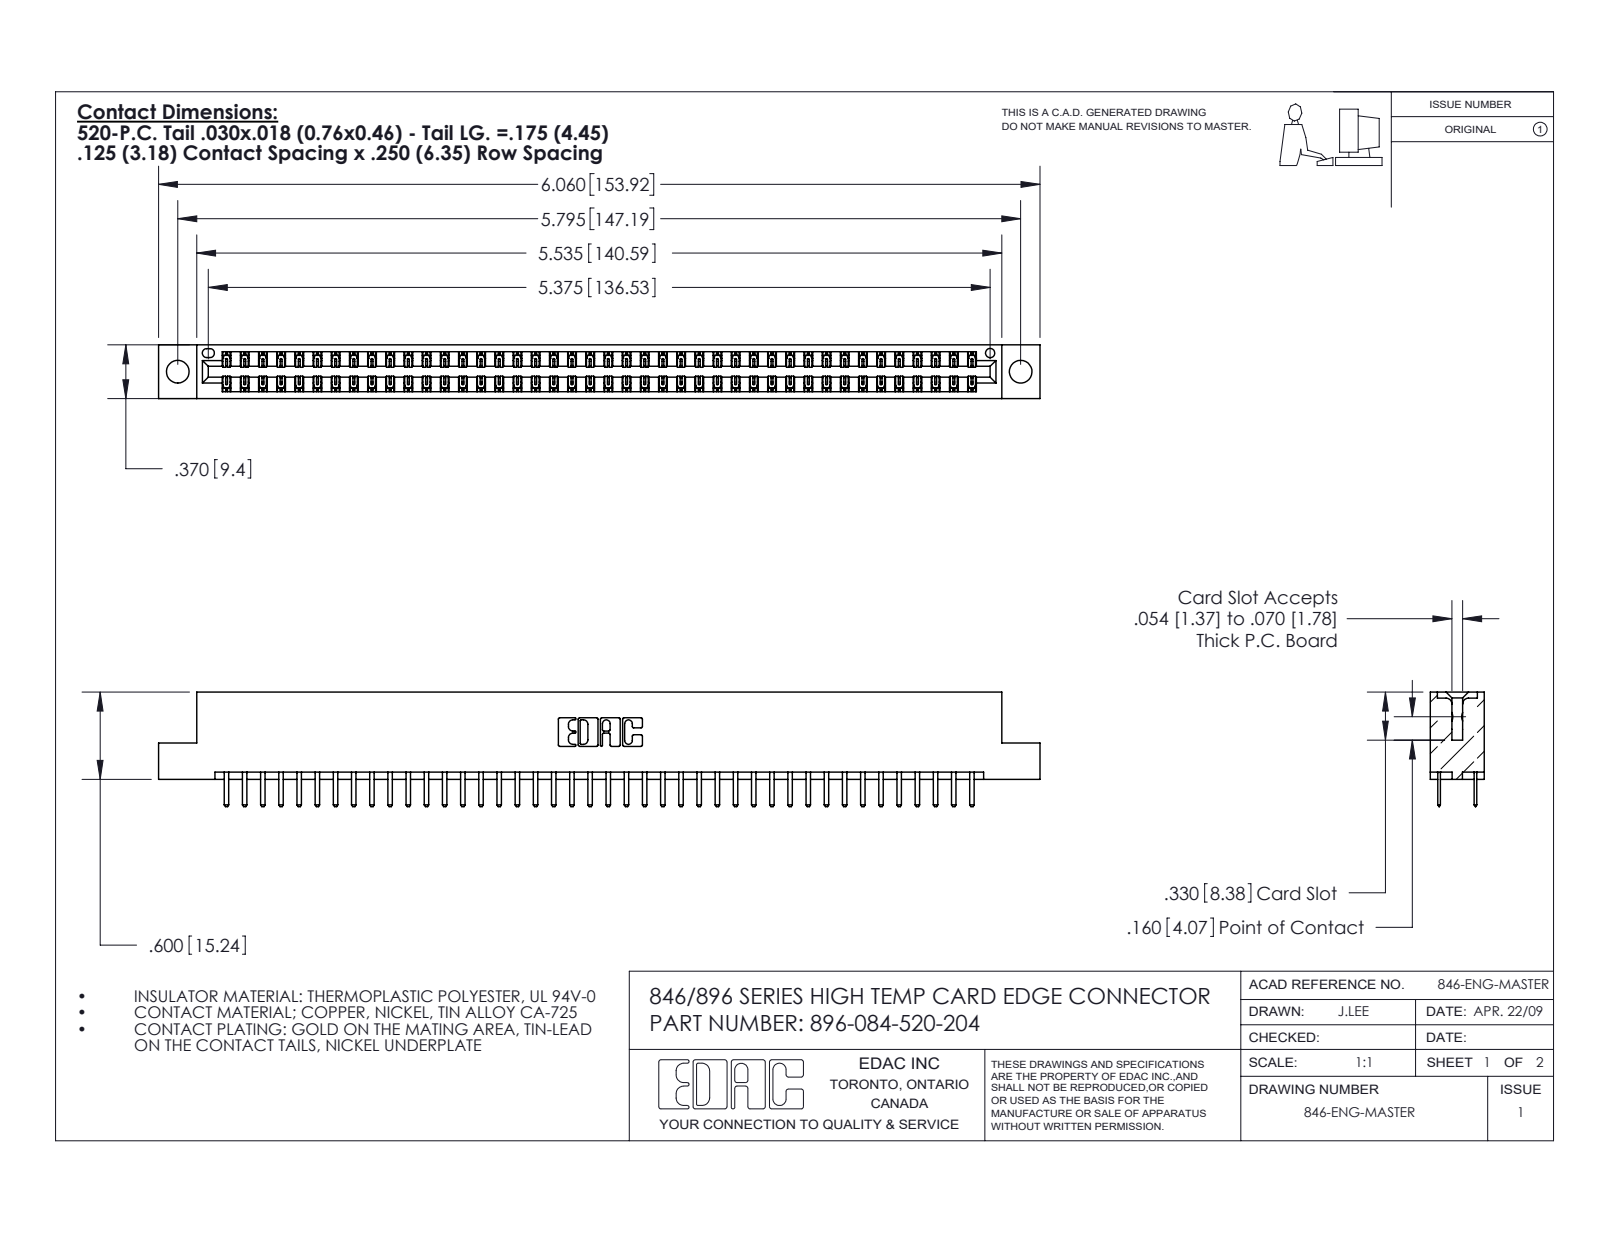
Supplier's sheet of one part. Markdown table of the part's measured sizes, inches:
| quantity | value |
| --- | --- |
| part name | 345-292-001_345-293-120; 396-084-520-204; 346 Part_Flush Mounting Lugs - 0.156 Dia-TH |
| STEP written by | SolidWorks 2016 (CONFIG_CONTROL_DESIGN) |
| units | inches |
| bodies | 85 solids, 4826 faces (3184 planar, 1642 cylindrical, 0 other) |
| overall size | 6.06 × 0.788 × 0.37 |
| volume | 0.908 in³ |
| surface area | 31.29 in² |
| round holes (diameter × count) | 0.156 × 2, 0.064 × 1 |
| partial cylindrical surfaces (radius × count) | 0.006 × 126, 0.01 × 88, 0.01 × 22, 0.007 × 6, 0.031 × 6, 0.026 × 3, 0.014 × 2, 0.022 × 2 |
| main face-to-face distances | 0.048, 0.322, 0.25, 0.37, 0.275, 0.072, 0.298, 0.025, 0.148, 0.222 |
| hole center spacings | 0.246, 5.586, 5.795 |
